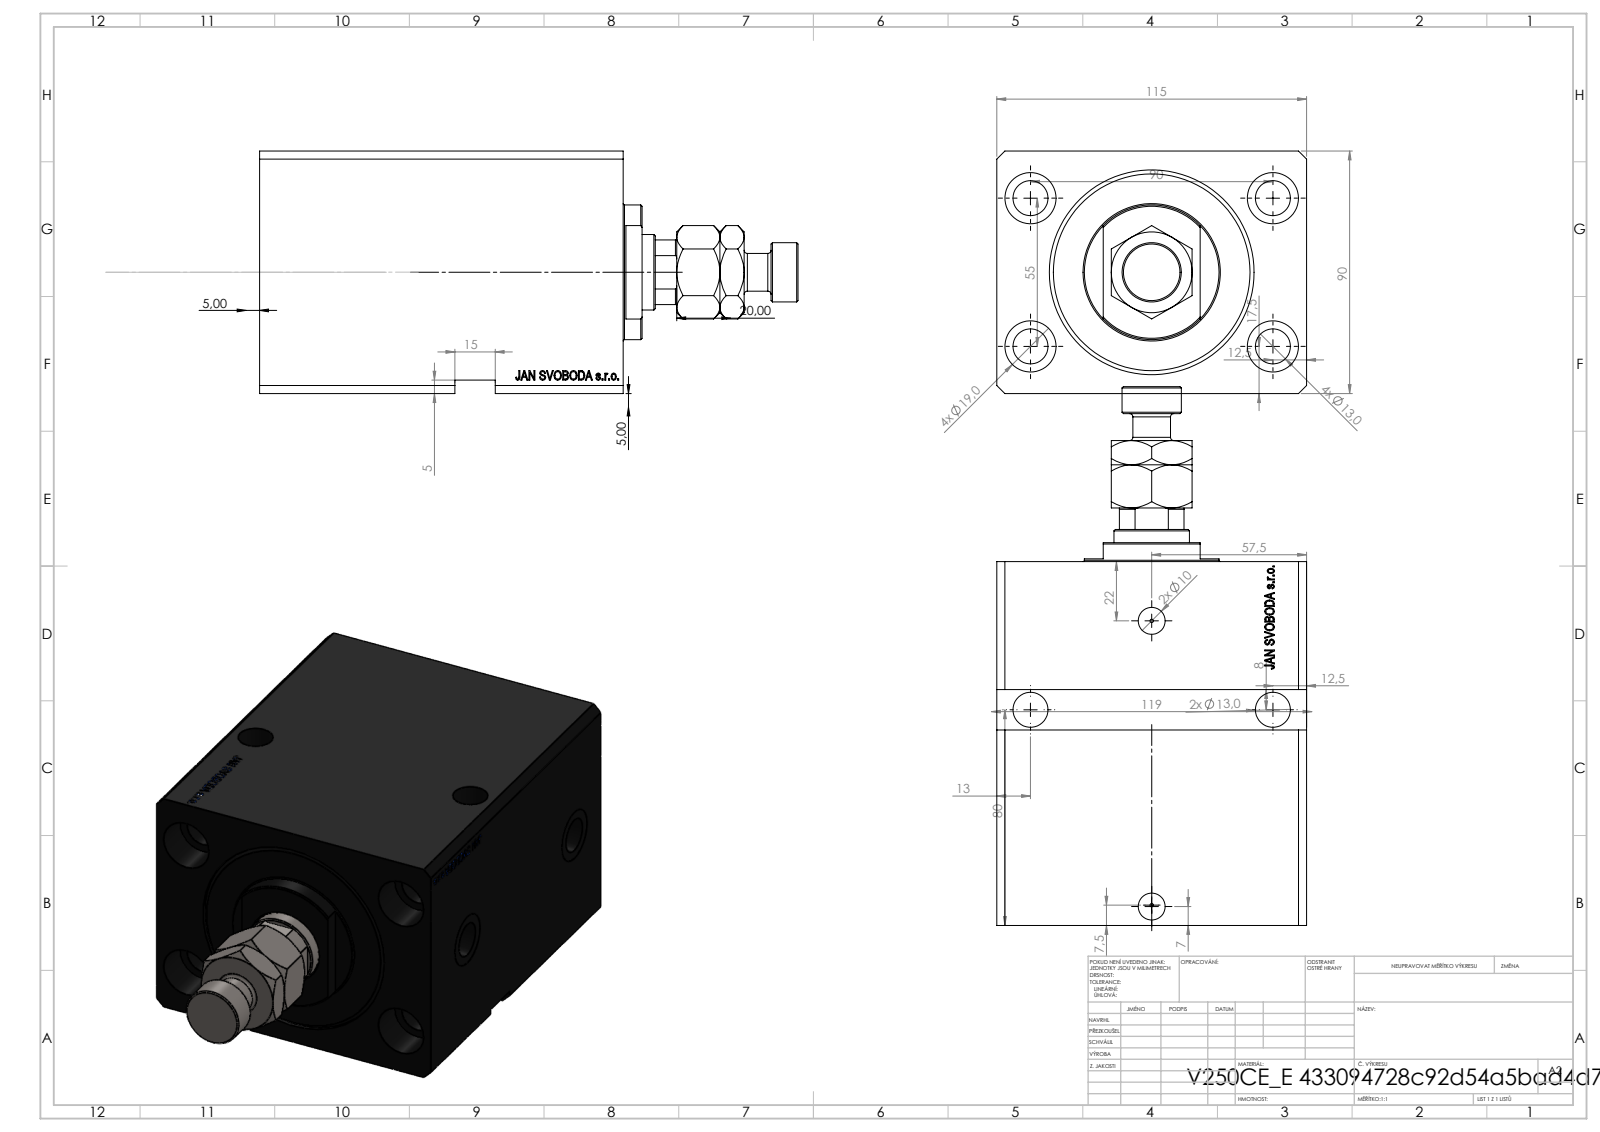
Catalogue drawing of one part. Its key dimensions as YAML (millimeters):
part_name: "V250CE_VC_E; MFA; V250CE_E_Body; V250CE_C_VCP"
step_written_by: "SolidWorks 2019 (CONFIG_CONTROL_DESIGN)"
units: millimeters
bodies: {solids: 4, faces: 1009, planar: 483, cylindrical: 108, other: 418}
overall_size: [200, 115, 90]
volume: 1169000
surface_area: 179473
round_holes:
  - {diameter: 13, count: 8}
  - {diameter: 1.25, count: 4}
  - {diameter: 19, count: 4}
  - {diameter: 10, count: 2}
  - {diameter: 13.16, count: 2}
  - {diameter: 20, count: 2}
  - {diameter: 18.5, count: 1}
  - {diameter: 28, count: 1}
  - {diameter: 63, count: 1}
  - {diameter: 76, count: 1}
round_bosses_or_shafts:
  - {diameter: 50, count: 1}
  - {diameter: 22, count: 1}
  - {diameter: 14, count: 1}
partial_cylinders:
  - {radius: 13.5, count: 1}
face_to_face_distances: [115, 90, 20, 135, 17.9, 117.1, 97.1, 65, 47.1, 50]
hole_center_spacings: [52.74, 55.8, 85.76, 90, 40, 55, 55.49, 85.3]
